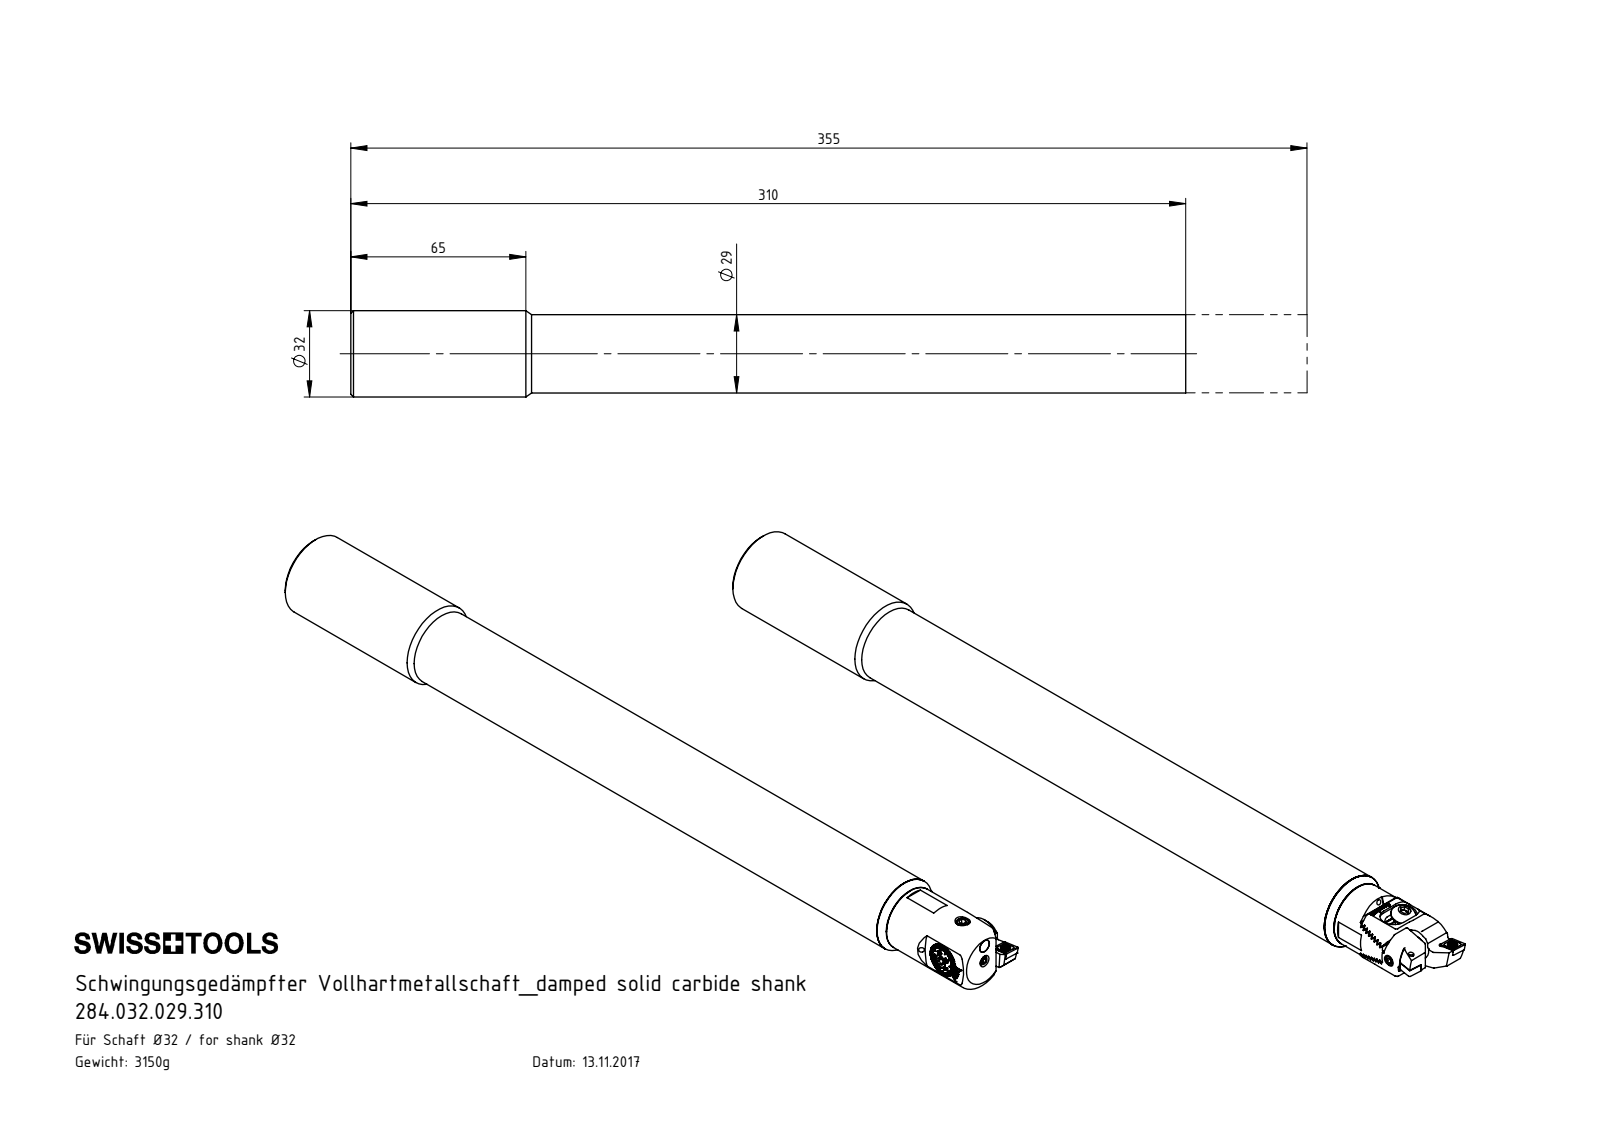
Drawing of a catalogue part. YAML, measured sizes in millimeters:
part_name: "HP5-ER1.019.036_A; U32-HP5.029.310_A; U32.HP5.029.310"
step_written_by: "SolidWorks 2017 (AUTOMOTIVE_DESIGN)"
units: millimeters
bodies: {solids: 2, faces: 25, planar: 6, cylindrical: 9, other: 10}
overall_size: [310, 32, 32]
volume: 204678
surface_area: 40183
round_holes:
  - {diameter: 4.2, count: 1}
  - {diameter: 14, count: 1}
  - {diameter: 17, count: 1}
  - {diameter: 17.5, count: 1}
  - {diameter: 19, count: 1}
round_bosses_or_shafts:
  - {diameter: 32, count: 1}
  - {diameter: 29, count: 1}
face_to_face_distances: [274, 310, 36, 300, 26, 10]
